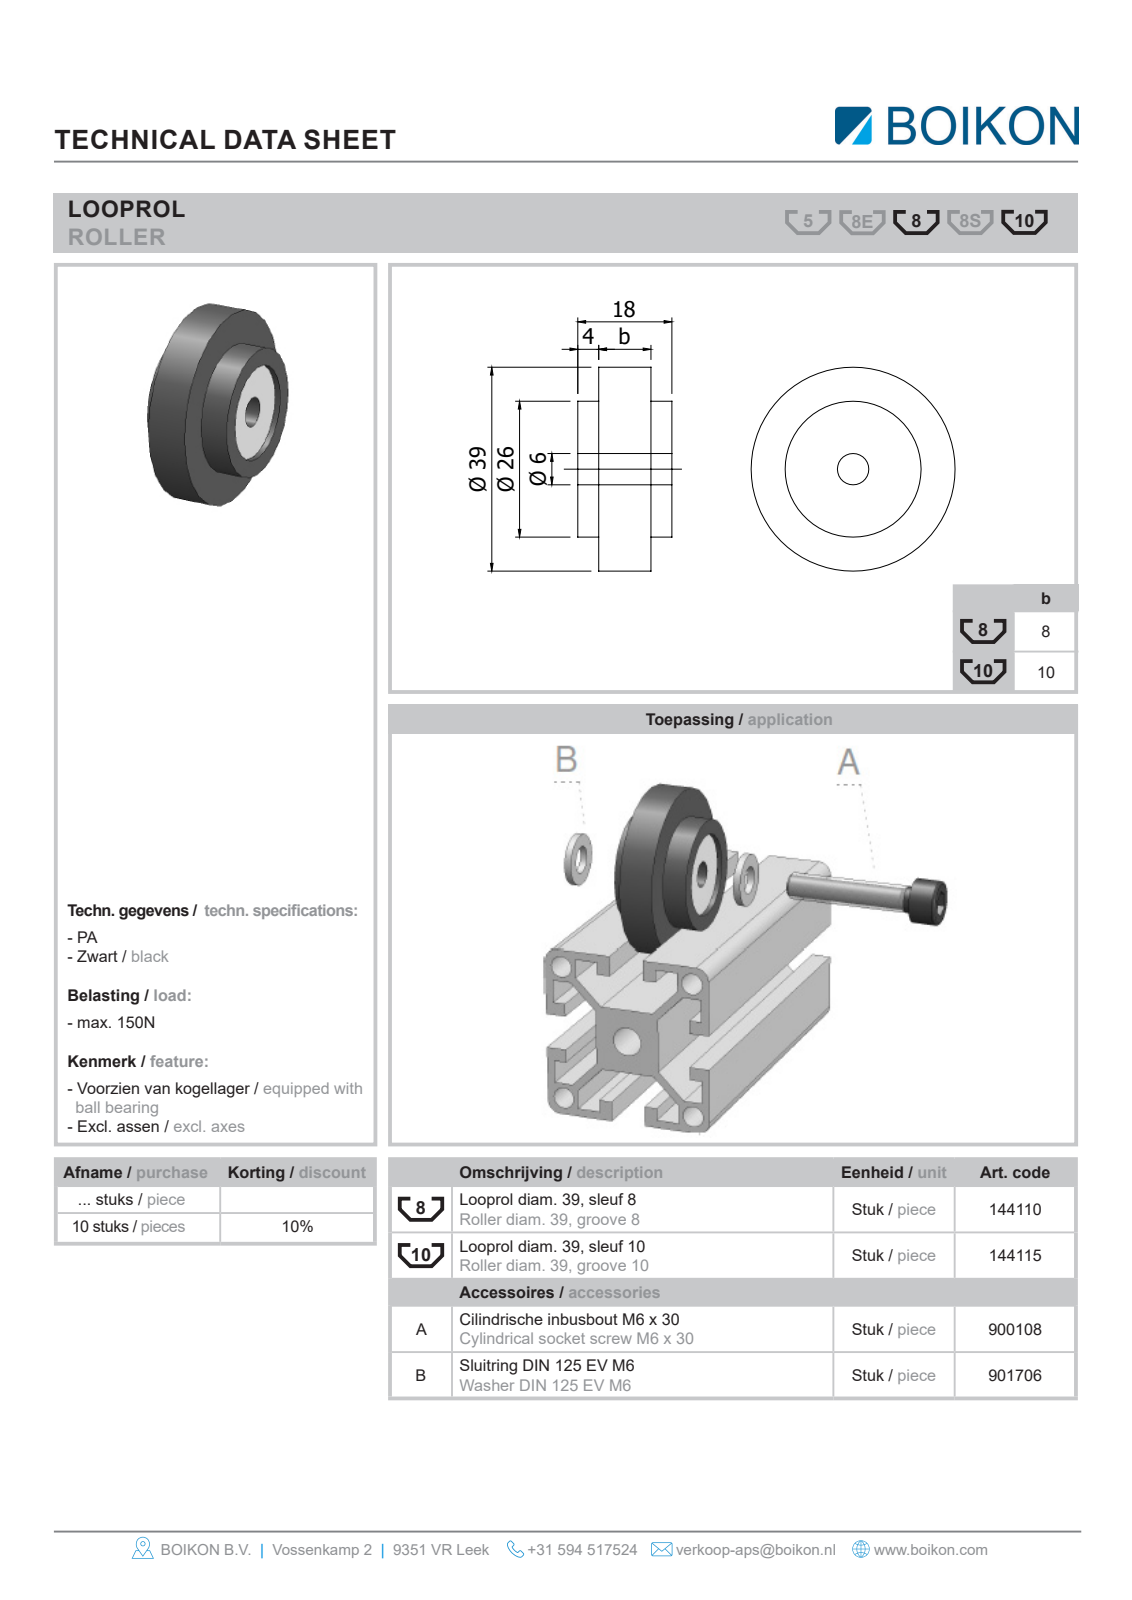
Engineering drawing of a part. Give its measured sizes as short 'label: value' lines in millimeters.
name: Root; 144115Looprol diam. 39, sleuf 10BOIKON
written by: HiCAD 2013 1802.4 Build 509 (AUTOMOTIVE_DESIGN)
unit: mm
bodies: 1 solid, 12 faces (6 planar, 6 cylindrical, 0 other)
size: 39 × 39 × 17.5
volume: 14 651 mm³; area: 4 581 mm²
holes: 1× ⌀6, 1× ⌀19
bosses: 1× ⌀39, 1× ⌀25.8
face distances: 9.8, 1.15, 16.35, 12.35, 2.55, 2.85, 12.65, 15.2, 13.5, 3.7
